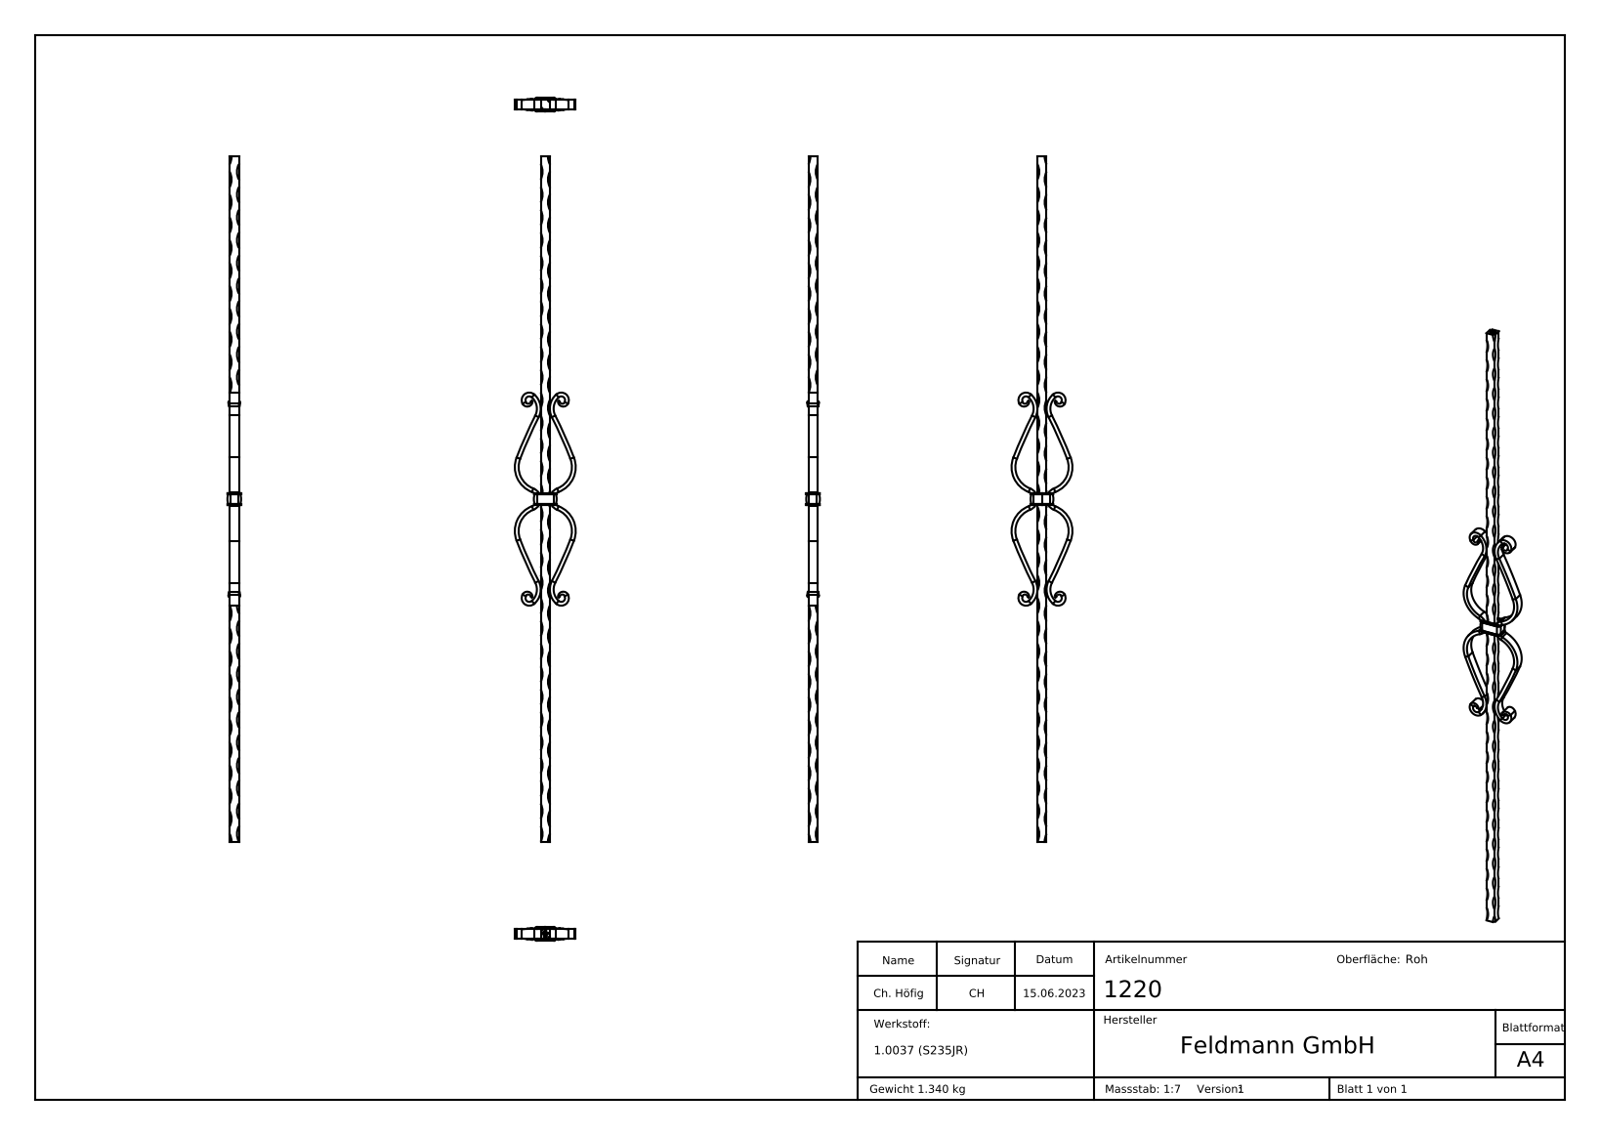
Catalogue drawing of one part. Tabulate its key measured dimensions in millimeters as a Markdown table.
| quantity | value |
| --- | --- |
| part name | 1220 |
| STEP written by | SolidWorks 2018 (CONFIG_CONTROL_DESIGN) |
| units | millimeters |
| bodies | 4 solids, 572 faces (208 planar, 93 cylindrical, 271 other) |
| overall size | 900 × 80 × 18 |
| volume | 171 773 mm³ |
| surface area | 71 152 mm² |
| partial cylindrical surfaces (radius × count) | 0.5 × 24, 0.2 × 8, 10 × 6, 1 × 4, 4 × 4, 5 × 4, 20 × 4, 20.14 × 4 |
| main face-to-face distances | 12, 18, 6, 442, 458, 16, 24, 900, 3, 443.5 |
